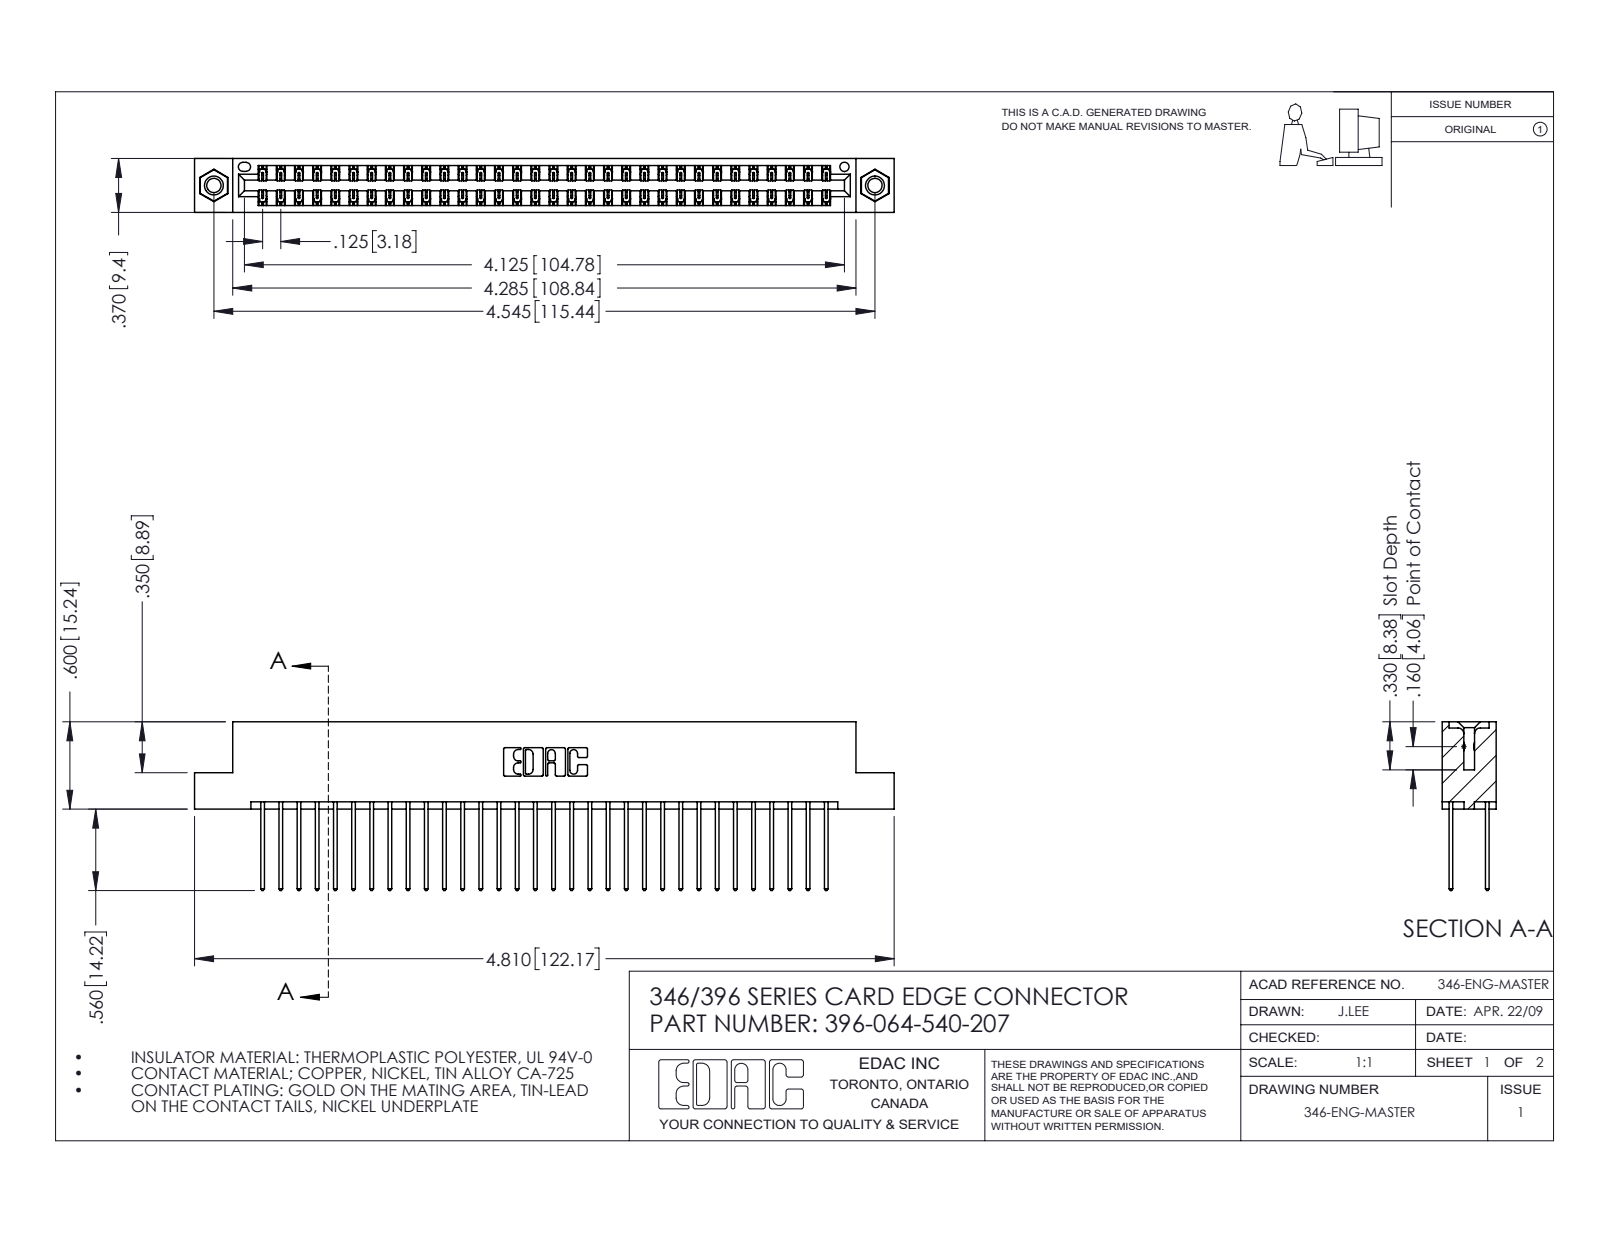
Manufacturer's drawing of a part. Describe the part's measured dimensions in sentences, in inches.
The part is named "346 Part_Flush Mounting Lugs - 0.156 Dia-TI; 345-292-001_345-293-140; 396-064-540-207; 345-250-001_345-250-005-103". Its 3-D file was written by "SolidWorks 2016 (CONFIG_CONTROL_DESIGN)". It is 67 solids with 3510 faces: 2348 planar, 1146 cylindrical and 16 other. Overall it measures 4.81 by 1.16 by 0.37 inches. Its volume is 0.736 cubic inches and its surface area 27.29 square inches. Round holes: 2 of diameter 0.098, 2 of diameter 0.125, 2 of diameter 0.156, 1 of diameter 0.064. Round bosses or shafts: 2 of diameter 0.155. Partial cylindrical surfaces (rounded edges, fillets, slot ends): 96 of radius 0.006, 64 of radius 0.01, 22 of radius 0.01, 6 of radius 0.007, 6 of radius 0.031, 3 of radius 0.026, 2 of radius 0.014, 2 of radius 0.022. The main face-to-face distances are 0.048, 0.322, 0.25, 0.072, 0.298, 0.025, 0.37, 0.275, 0.148, 0.222. The hole center spacings are 0.246, 4.337, 4.545.
